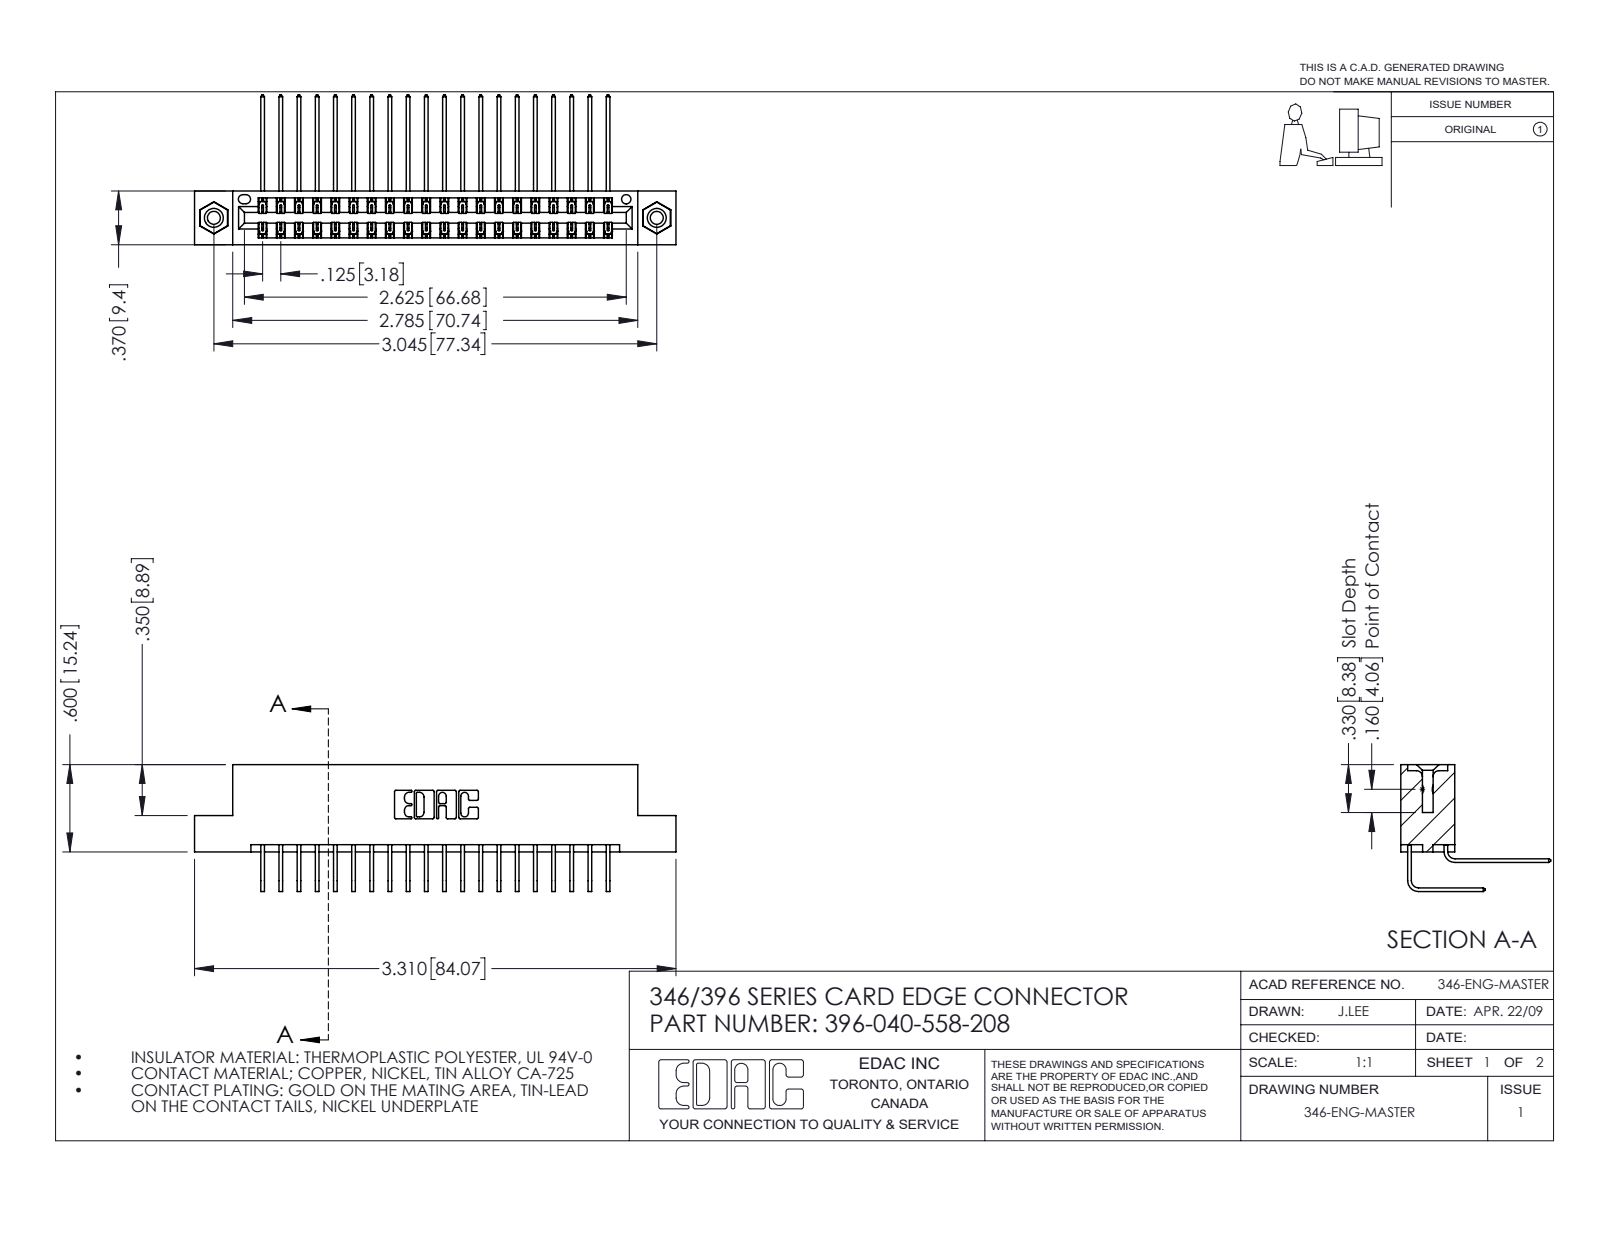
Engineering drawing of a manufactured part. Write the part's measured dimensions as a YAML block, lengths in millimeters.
part_name: "345-292-001_558 559 Tail - 1; 346 Part_Flush Mounting Lugs - 0.156 Dia-TI; 345-250-001_345-250-003-102; 345-292-001_558 Tail - 2 (+1 more)"
step_written_by: "SolidWorks 2016 (CONFIG_CONTROL_DESIGN)"
units: millimeters
bodies: {solids: 43, faces: 2342, planar: 1588, cylindrical: 738, other: 16}
overall_size: [84.1, 26.2, 22.2]
volume: 8260
surface_area: 12120
round_holes:
  - {diameter: 2.3, count: 2}
  - {diameter: 3.2, count: 2}
  - {diameter: 4, count: 2}
  - {diameter: 1.6, count: 1}
round_bosses_or_shafts:
  - {diameter: 3.9, count: 2}
partial_cylinders:
  - {radius: 0.2, count: 60}
  - {radius: 0.3, count: 22}
  - {radius: 0.2, count: 6}
  - {radius: 0.8, count: 6}
  - {radius: 0.7, count: 3}
  - {radius: 0.4, count: 2}
  - {radius: 0.6, count: 2}
  - {radius: 0.6, count: 2}
face_to_face_distances: [8.2, 1.2, 6.4, 0.6, 9.4, 7.6, 1.8, 7, 3.8, 5.6]
hole_center_spacings: [6.2, 72.1, 77.3]
